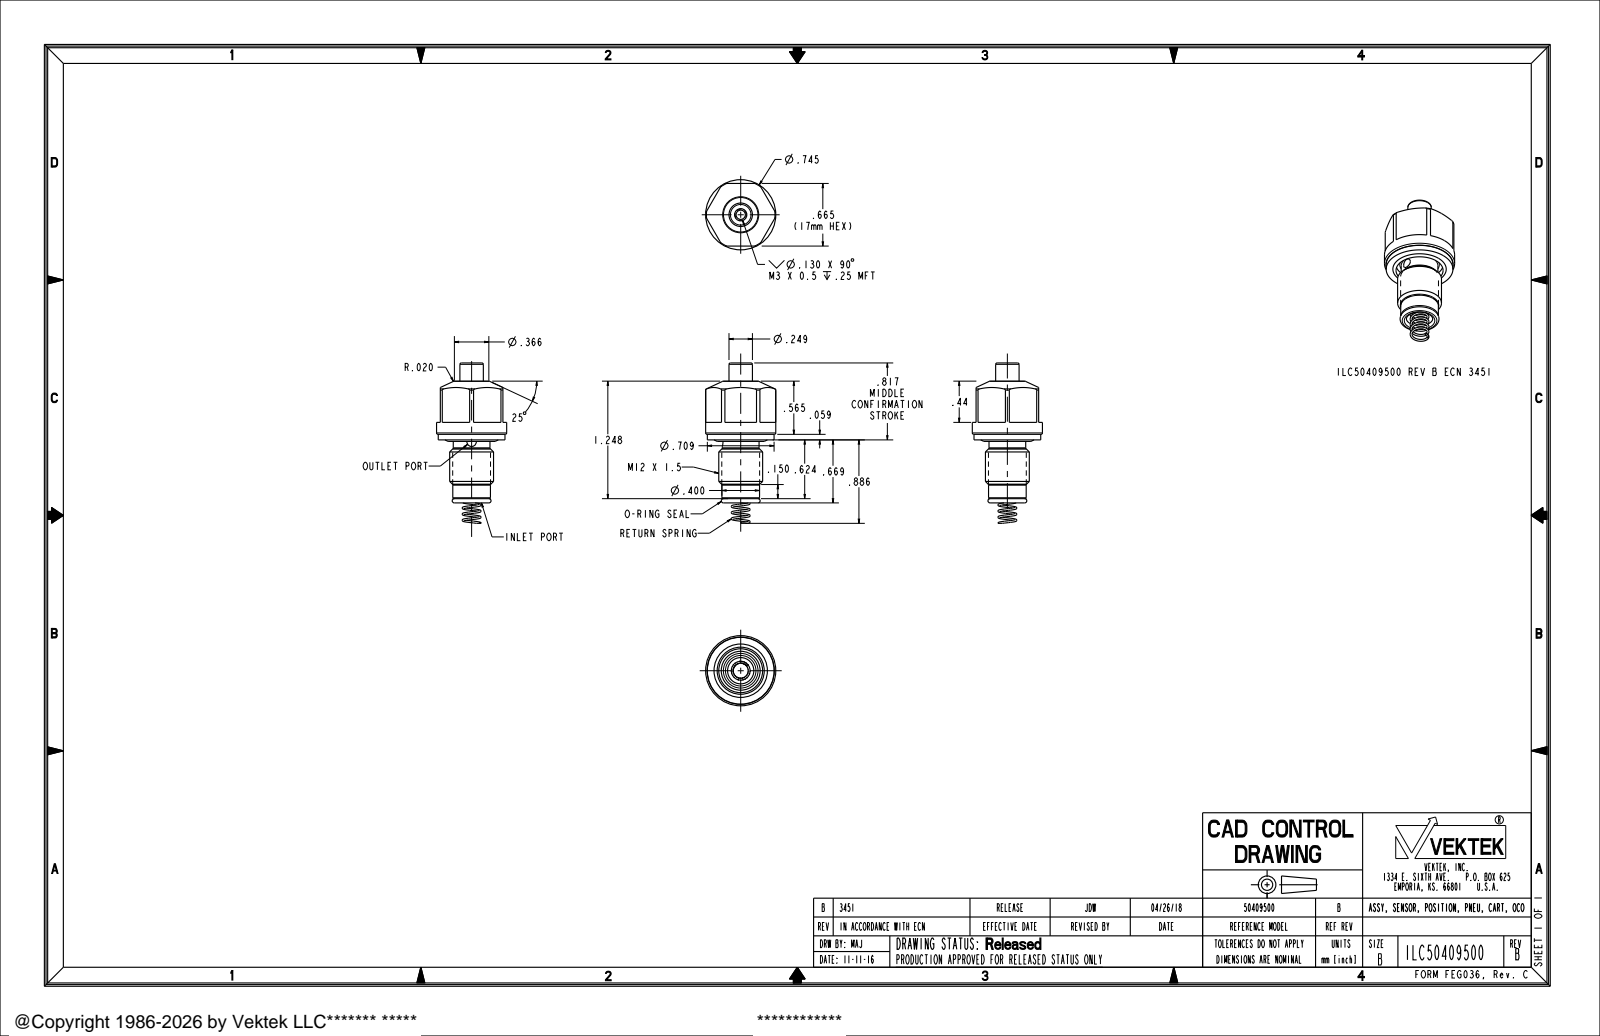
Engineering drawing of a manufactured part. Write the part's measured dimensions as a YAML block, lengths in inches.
part_name: "ILC50409500"
step_written_by: "PRO/ENGINEER BY PARAMETRIC TECHNOLOGY CORPORATION, 2013320 (AUTOMOTIVE_DESIGN)"
units: inches
bodies: {solids: 1, faces: 92, planar: 26, cylindrical: 24, other: 42}
overall_size: [1.703, 0.745, 0.745]
volume: 0.31
surface_area: 4.867
round_holes:
  - {diameter: 0.098, count: 1}
  - {diameter: 0.1, count: 1}
  - {diameter: 0.118, count: 1}
  - {diameter: 0.312, count: 1}
  - {diameter: 0.5, count: 1}
round_bosses_or_shafts:
  - {diameter: 0.745, count: 1}
  - {diameter: 0.709, count: 1}
  - {diameter: 0.466, count: 1}
  - {diameter: 0.402, count: 1}
  - {diameter: 0.4, count: 1}
  - {diameter: 0.39, count: 1}
  - {diameter: 0.249, count: 1}
face_to_face_distances: [0.665, 0.324, 0.624, 0.383, 0.059, 0.948, 0.565, 0.51, 0.186, 0.127]
